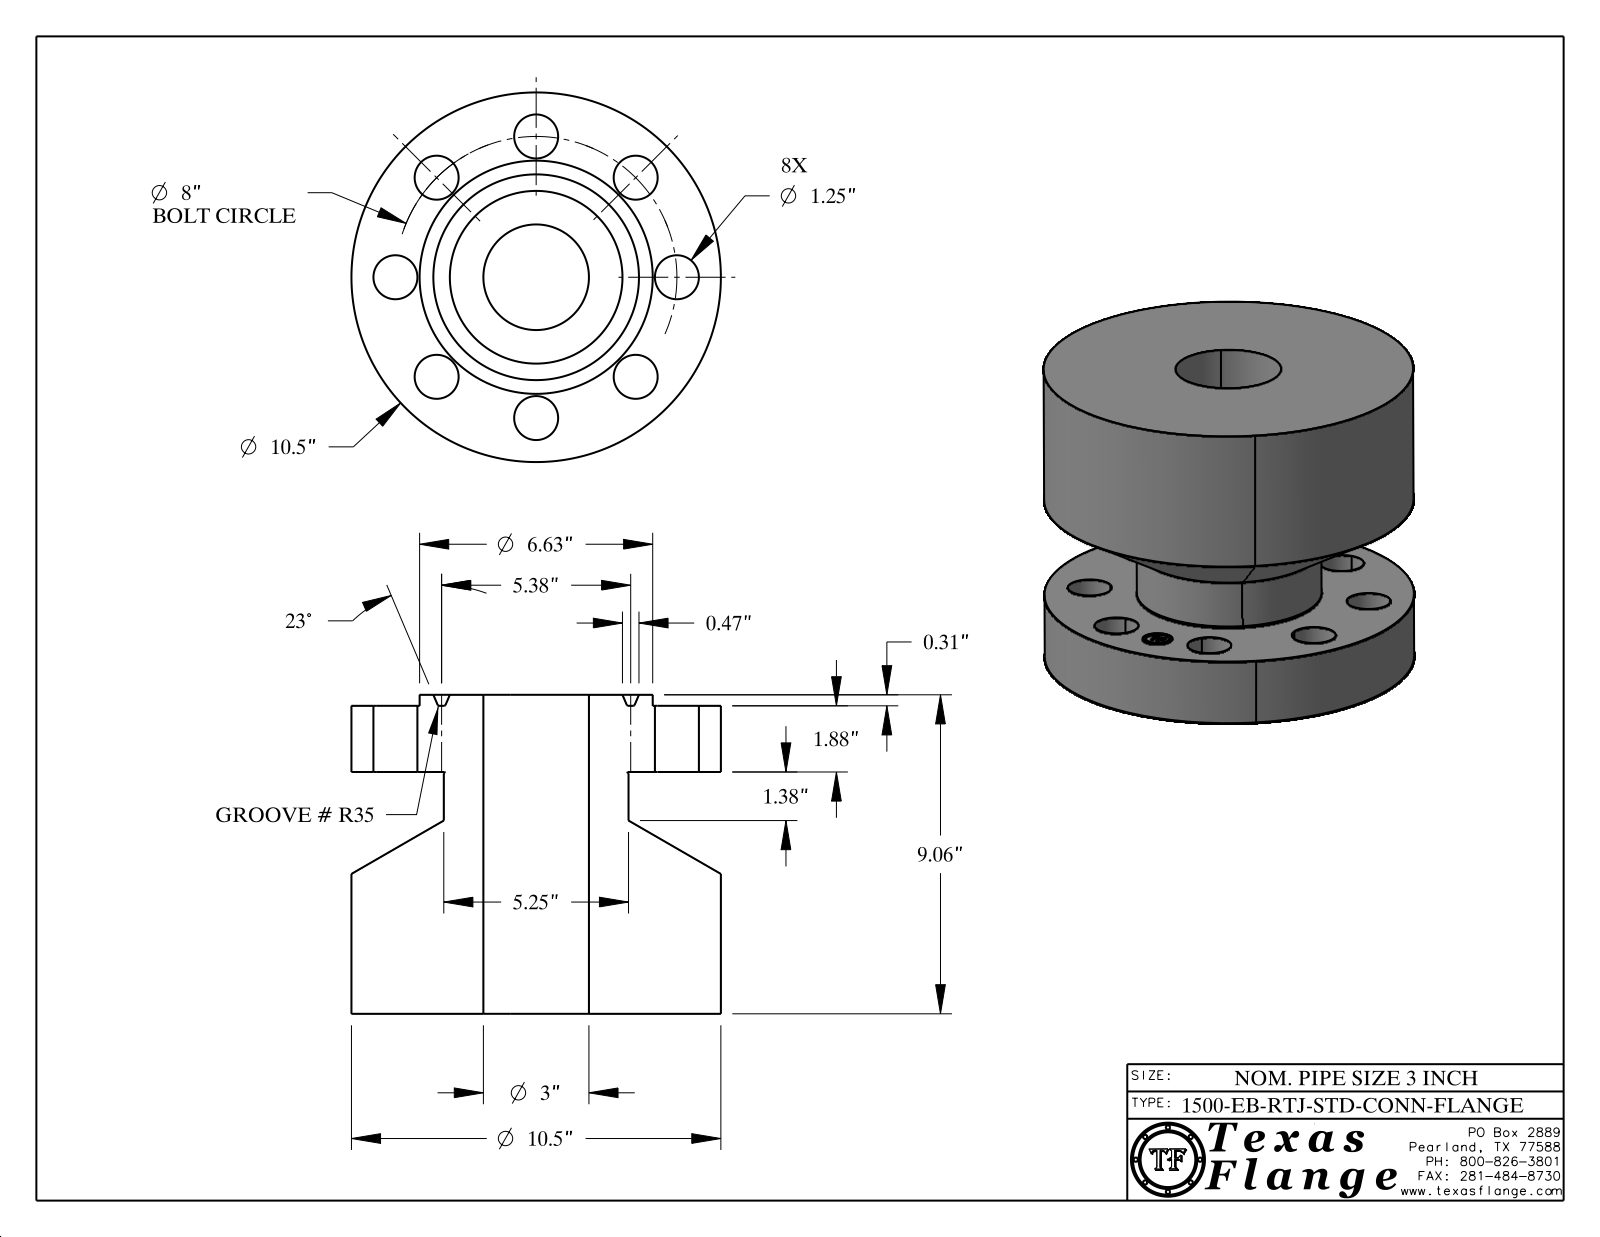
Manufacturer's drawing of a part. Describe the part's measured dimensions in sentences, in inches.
The part is named "3-1500-EB-RTJ-STD-CONN-FLANGE". Its 3-D file was written by "CATIA V5 STEP AP214 (AUTOMOTIVE_DESIGN)". It is 1 solid with 431 faces: 371 planar, 46 cylindrical and 14 other. Overall it measures 10.5 by 10.5 by 9.063 inches. Its volume is 539.8 cubic inches and its surface area 653.7 square inches. Round holes: 8 of diameter 1.25, 1 of diameter 0.85, 1 of diameter 3. Round bosses or shafts: 8 of diameter 0.051, 1 of diameter 10.5, 1 of diameter 6.625, 1 of diameter 5.25, 1 of diameter 0.67. The main face-to-face distances are 6.87, 1.88, 8.75, 0.313, 2.193, 9.063, 2.188, 1.875, 6.875, 0.254. The hole center spacings are 4, 3.061, 5.657, 7.391, 1.561, 6.652, 7.846, 8.
